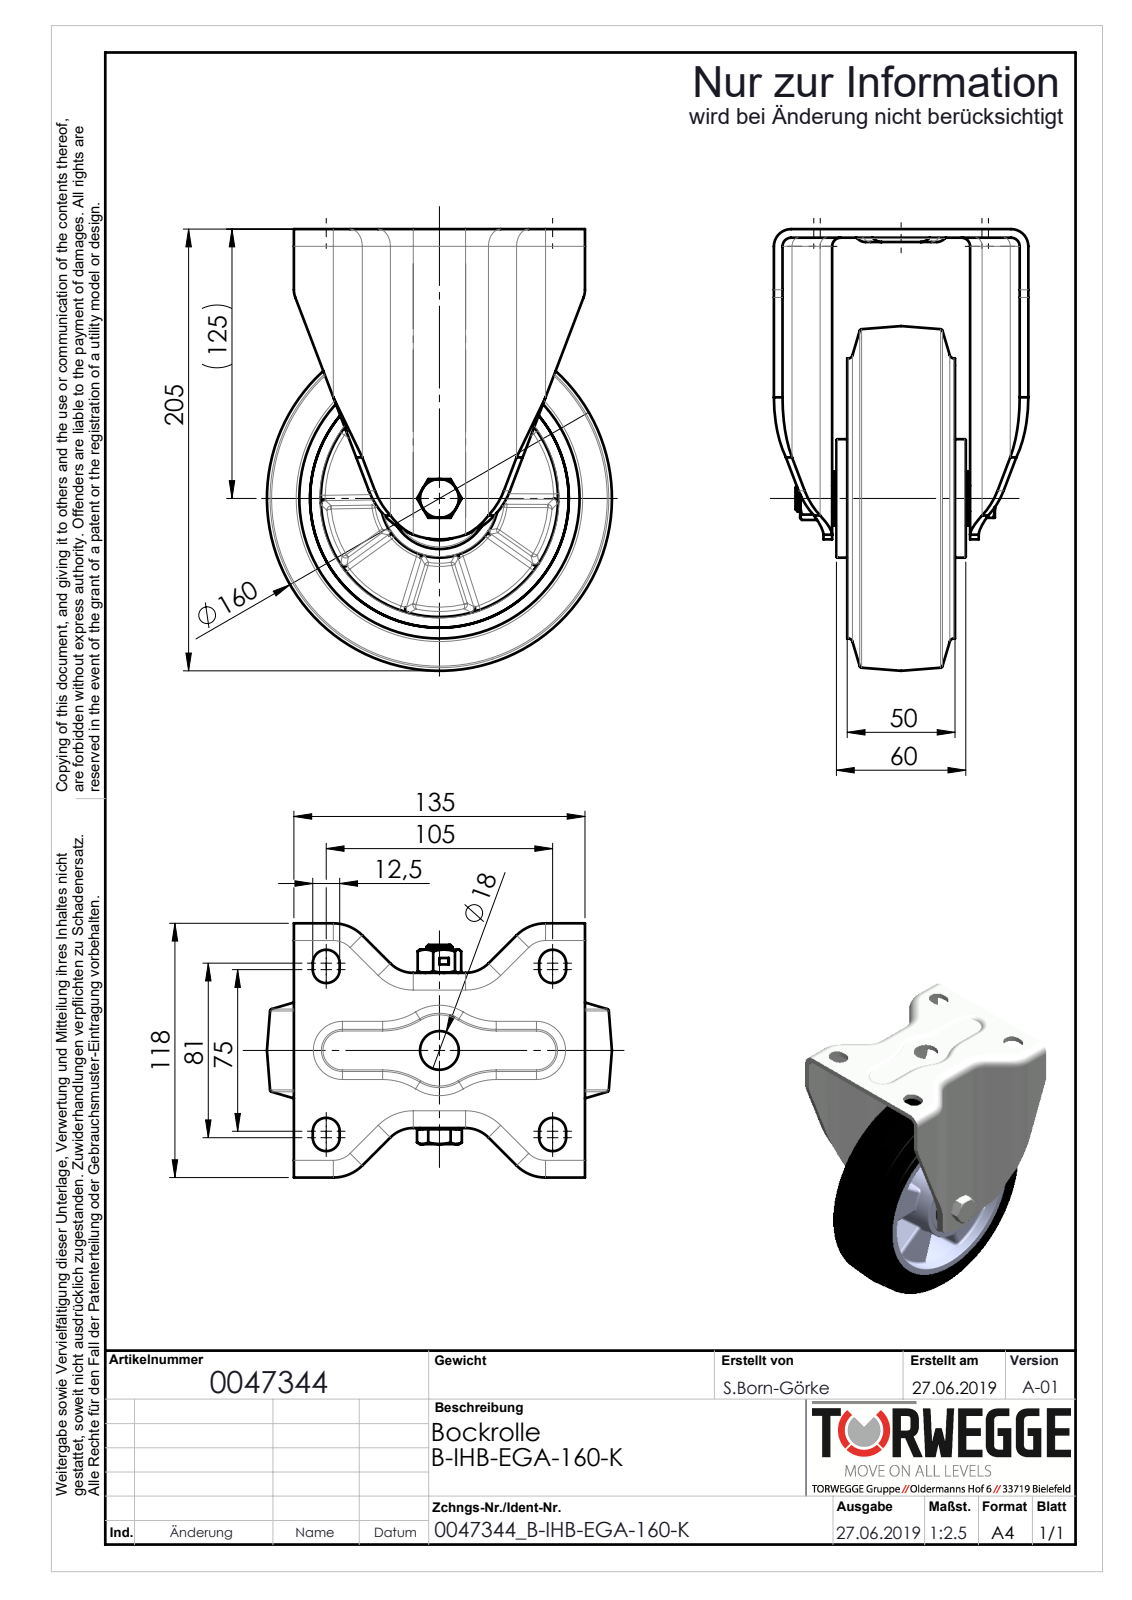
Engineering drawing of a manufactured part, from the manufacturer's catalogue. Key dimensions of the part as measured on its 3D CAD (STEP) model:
Part name (STEP PRODUCT): 0047344_B-IHB-EGA-160-K_(A-01)
STEP written by: SolidWorks 2018 (AUTOMOTIVE_DESIGN)
Units: millimetres
Bodies: 14 solids, 755 faces (152 planar, 198 cylindrical, 405 other)
Overall size (bounding box): 205 × 160 × 118
Volume: 802 282 mm³ · Surface area: 263 375 mm²
Round holes (diameter × count): ⌀10.2 ×1, ⌀12 ×1, ⌀12.2 ×1, ⌀12.5 ×1, ⌀18 ×1, ⌀20 ×1, ⌀21 ×1, ⌀28.1 ×1, ⌀38 ×1, ⌀38.9 ×1, ⌀47 ×1, ⌀110 ×1
Round bosses / shafts (diameter × count): ⌀130 ×1, ⌀55 ×1, ⌀25 ×1, ⌀19.9 ×1, ⌀18 ×1
Partial cylindrical surfaces — rounded edges, fillets, slot ends (radius × count): R1.5 ×20, R2.5 ×20, R4 ×8, R6.25 ×8, R8 ×8, R15 ×8, R19 ×8, R1 ×4
Main face-to-face distances: 4, 2, 15.5, 20.96, 23, 91, 44.5, 11, 61, 68
